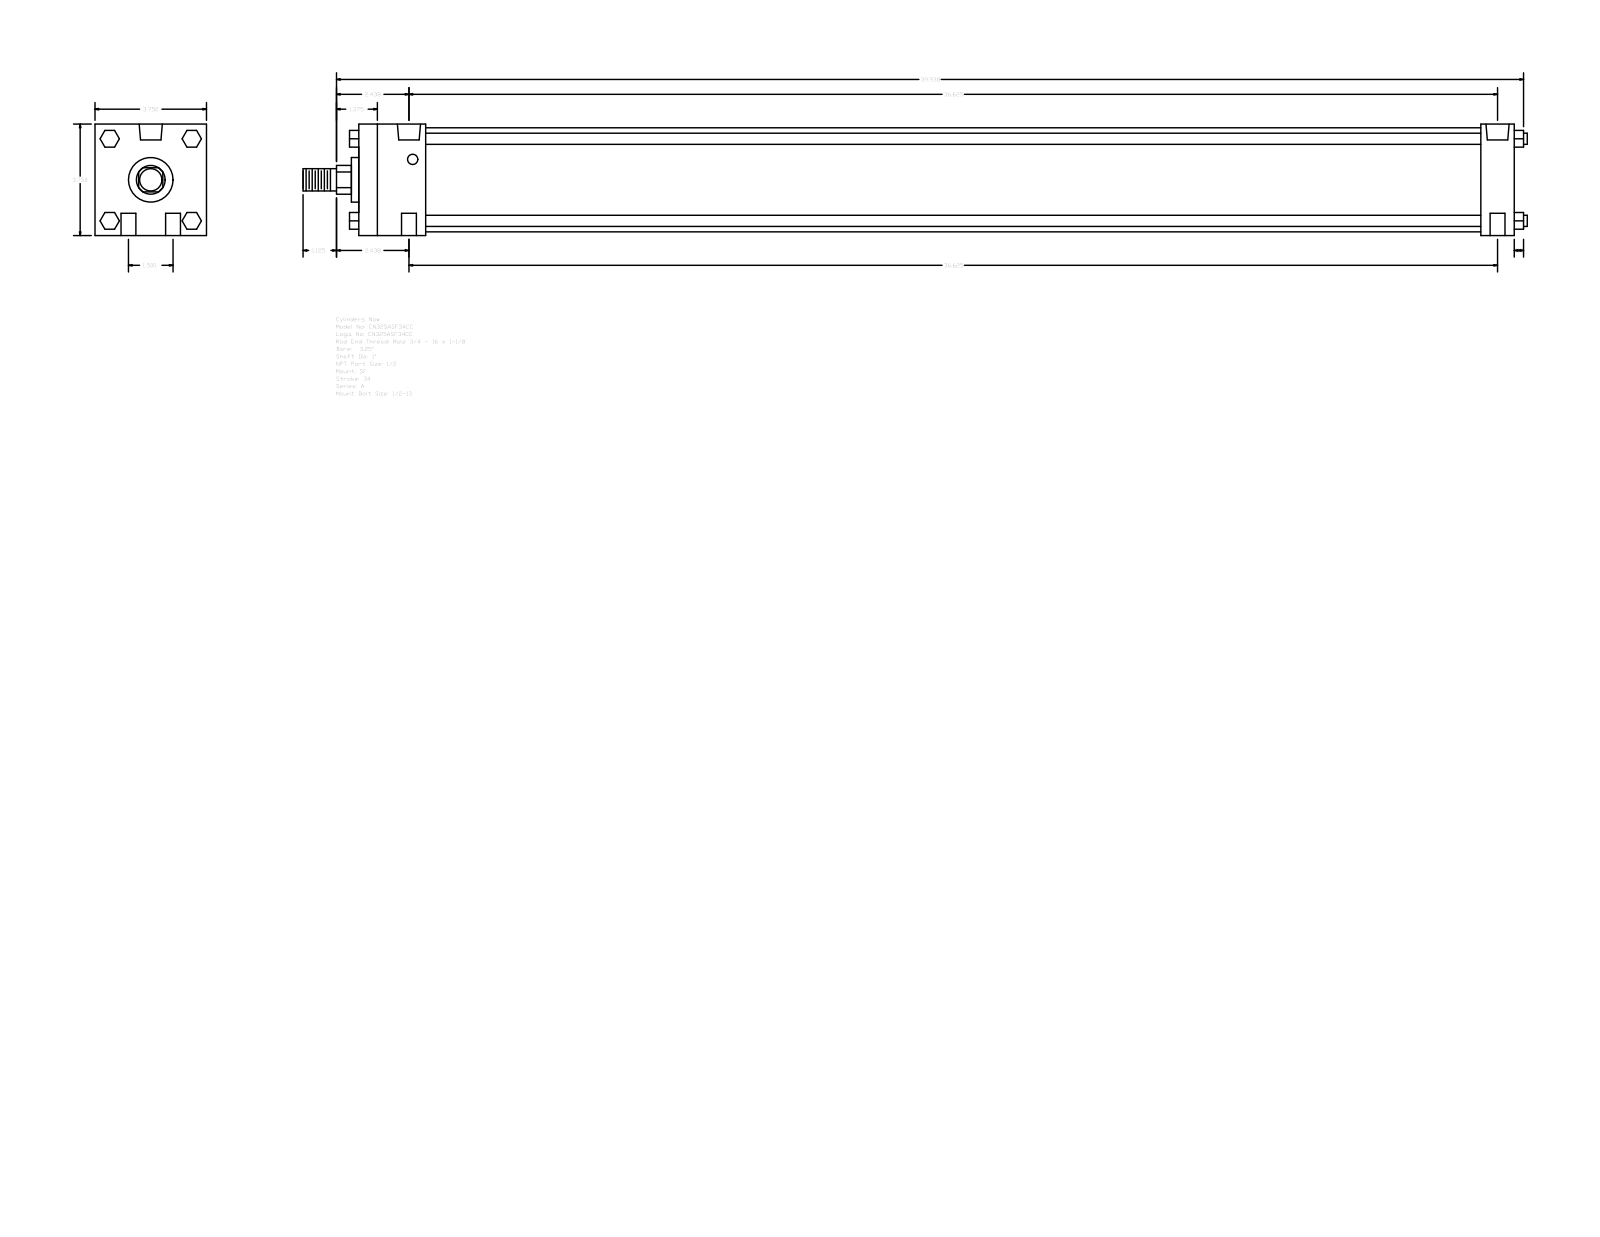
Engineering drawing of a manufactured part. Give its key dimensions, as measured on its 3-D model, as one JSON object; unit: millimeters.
{"part_name": "A_SF__0325_1", "step_written_by": "GSSL Pune (CONFIG_CONTROL_DESIGN)", "units": "millimeters", "bodies": {"solids": 0, "faces": 124, "planar": 94, "cylindrical": 30, "other": 0}, "overall_size": [1046.16, 95.25, 95.25], "round_holes": [[12.7, 4], [8.73, 2], [19.77, 2]], "round_bosses_or_shafts": [[9.53, 4], [88.9, 1], [38.1, 1], [25.4, 1], [19.05, 1]], "partial_cylinders_radius": [[12.29, 1]], "face_to_face_distances": [95.24, 987.43, 958.85, 28.58, 57.15, 901.7, 930.28, 14.28, 35.05, 60.71], "hole_center_spacings": [19.05, 930.48, 930.28, 38.1, 931.06, 923.92]}
